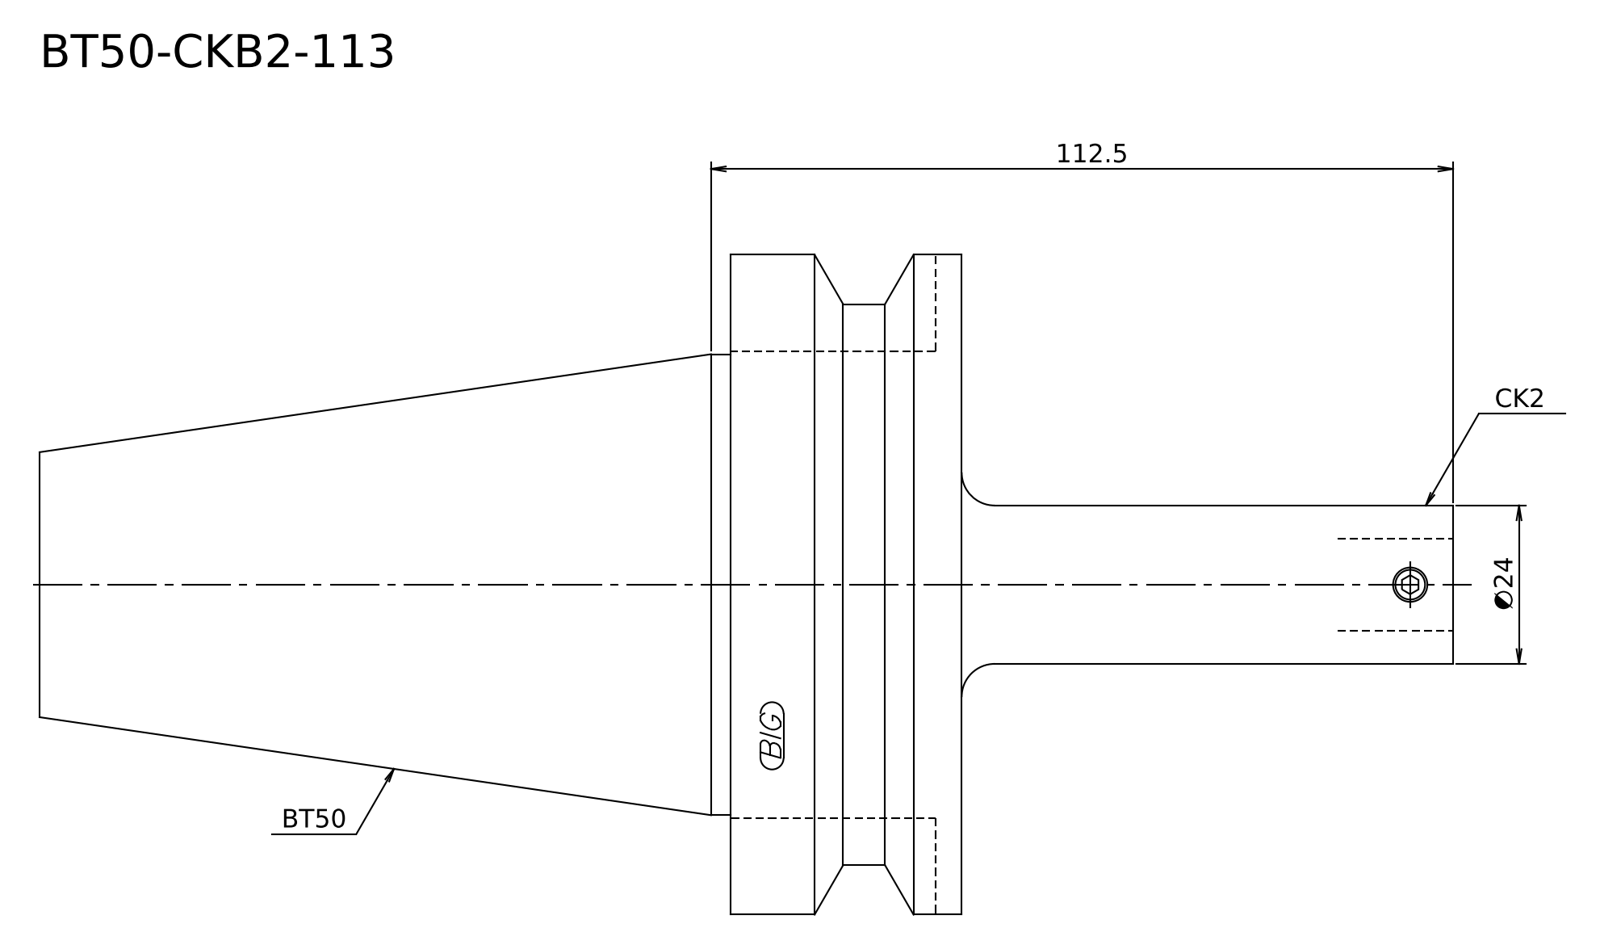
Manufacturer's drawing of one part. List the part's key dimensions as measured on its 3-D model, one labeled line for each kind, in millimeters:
STEP written by: Kubotek KeyCreator V8.5.1 (14335) (CONFIG_CONTROL_DESIGN)
Units: millimetres
Bodies: 1 solid, 13 faces (4 planar, 5 cylindrical, 4 other)
Overall size (bounding box): 214.3 × 100 × 100
Volume: 545 422 mm³ · Surface area: 50 016 mm²
Round bosses / shafts (diameter × count): ⌀100 ×1, ⌀85 ×1, ⌀69.85 ×1, ⌀24 ×1
Main face-to-face distances: 35, 139.8, 104.8, 74.5, 109.5, 214.3
